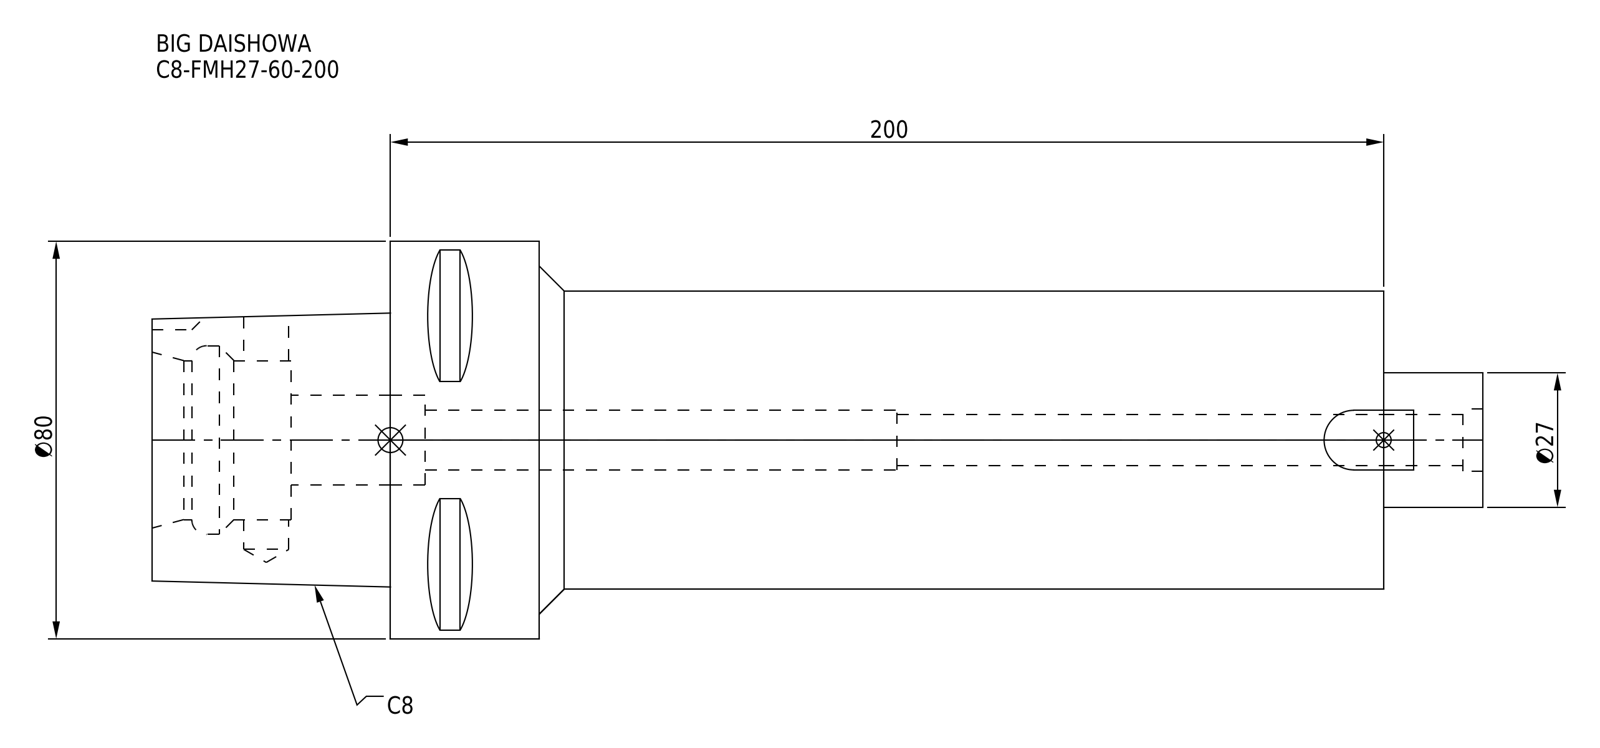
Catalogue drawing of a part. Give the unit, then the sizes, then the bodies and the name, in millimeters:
Units: millimetres
Overall size (bounding box): 268 × 80 × 80
Round holes (diameter × count): ⌀9.1 ×1, ⌀10.3 ×1, ⌀12 ×1, ⌀12.5 ×1, ⌀18 ×1, ⌀32 ×1, ⌀38 ×1
Round bosses / shafts (diameter × count): ⌀80 ×1, ⌀60 ×1, ⌀27 ×1
Partial cylindrical surfaces — rounded edges, fillets, slot ends (radius × count): R6 ×1
Main face-to-face distances: 200, 170, 30, 248, 78, 48, 20, 220, 28, 50
Volume: 698 707 mm³ · Surface area: 72 087 mm²
Bodies: 1 solid, 78 faces (41 planar, 25 cylindrical, 12 other)
Part name (STEP PRODUCT): C8-FMH27-60-200
STEP written by: CREO PARAMETRIC BY PTC INC, 2016380 (AUTOMOTIVE_DESIGN)
